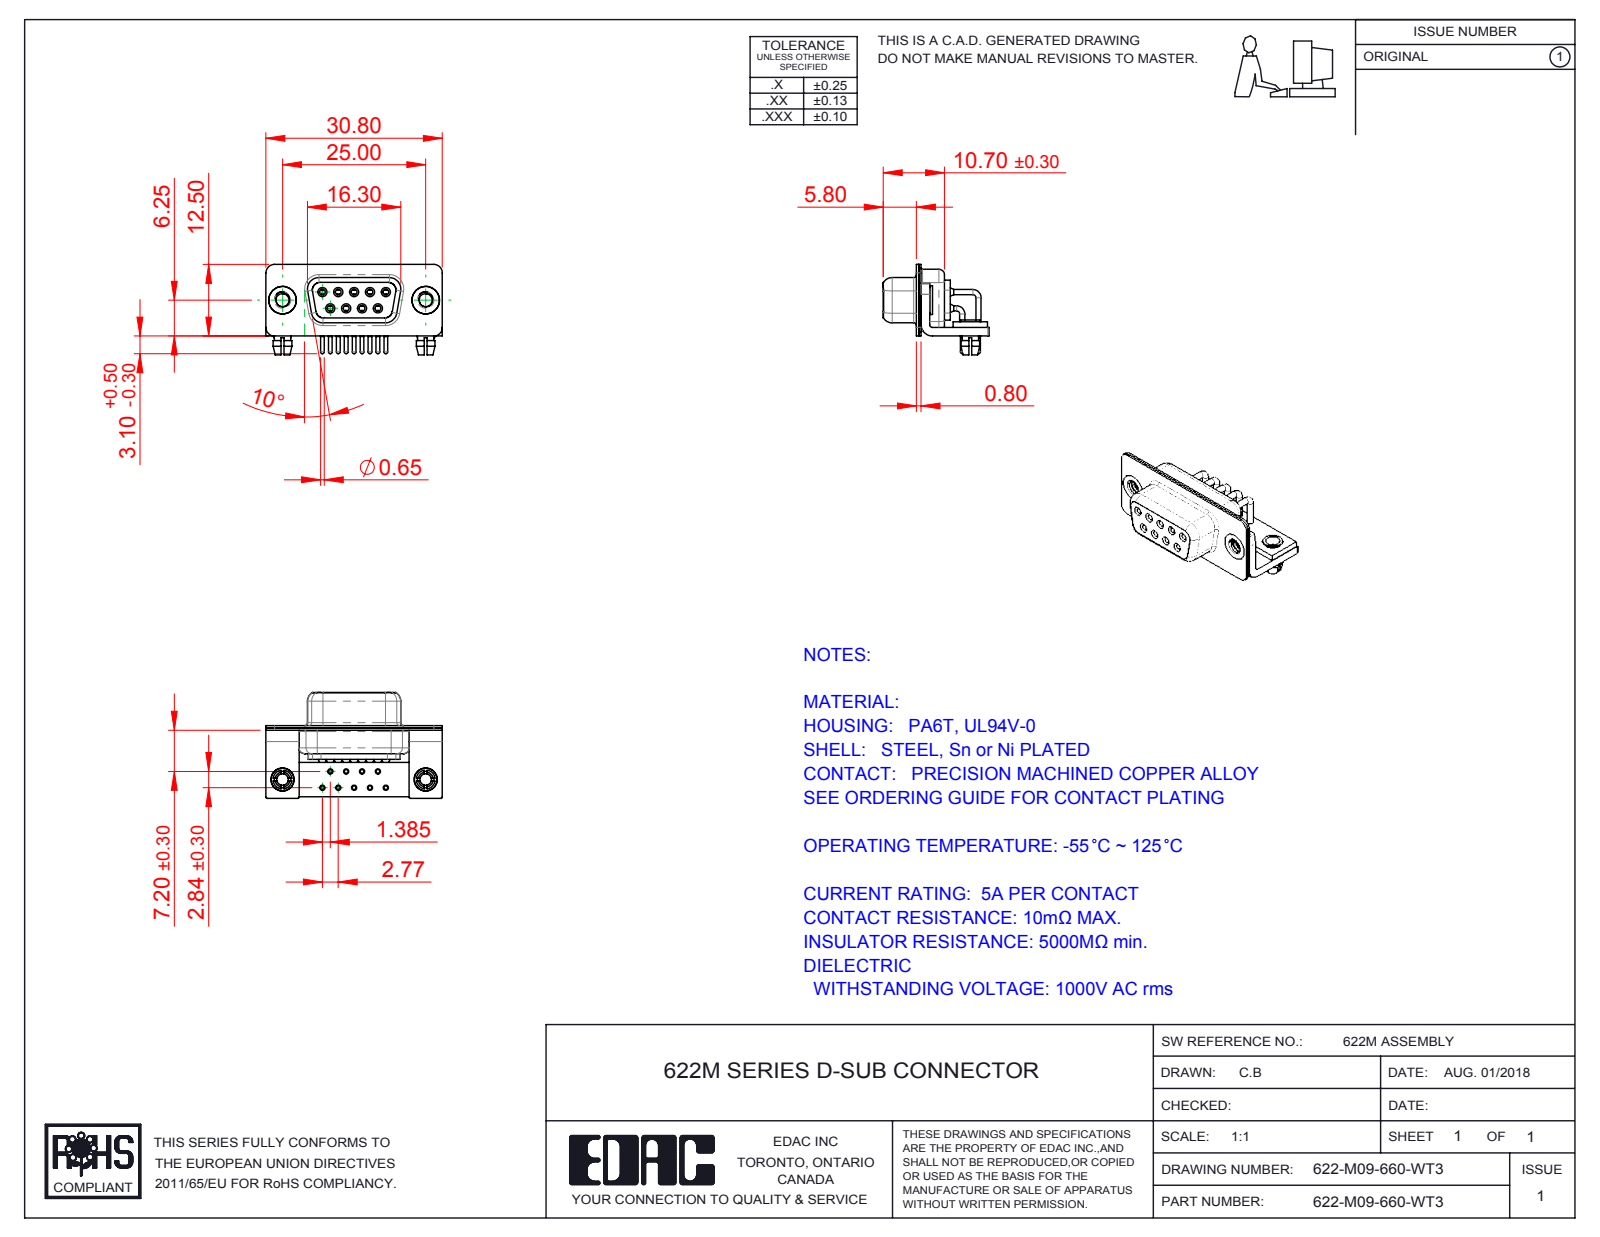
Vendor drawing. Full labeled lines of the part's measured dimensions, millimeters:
Part name (STEP PRODUCT): 622M Stabilizer Bracket; 622M 4-40 Threaded Rivet_Stabilizer; 622M Contact Row 2; 622M Contact Row 1 (+6 more)
STEP written by: SolidWorks 2016 (CONFIG_CONTROL_DESIGN)
Units: millimetres
Bodies: 19 solids, 916 faces (276 planar, 416 cylindrical, 224 other)
Overall size (bounding box): 30.8 × 18.5 × 15.8
Volume: 2 177 mm³ · Surface area: 5 763 mm²
Round holes (diameter × count): ⌀2 ×11, ⌀0.9 ×9, ⌀1 ×9, ⌀1.1 ×9, ⌀1.7 ×9, ⌀1.8 ×9, ⌀2.26 ×2, ⌀2.5 ×2, ⌀3.2 ×2, ⌀4 ×2, ⌀4.8 ×2
Round bosses / shafts (diameter × count): ⌀1.6 ×9, ⌀1.5 ×9, ⌀0.9 ×9, ⌀0.65 ×9, ⌀5 ×2, ⌀4.9 ×2, ⌀4 ×2, ⌀3.4 ×2
Partial cylindrical surfaces — rounded edges, fillets, slot ends (radius × count): R0.25 ×16, R1.5 ×16, R2 ×13, R1.35 ×8, R1.6 ×8, R0.5 ×5, R0.6 ×4, R0.65 ×4
Main face-to-face distances: 0.4, 0.8, 1.5, 2.3, 1.9, 1, 9.35, 1.45, 8.95, 0.85
Hole centre spacings: 3.16, 2.77, 5.54, 5.03, 5.04, 8.31, 7.48, 7.49
